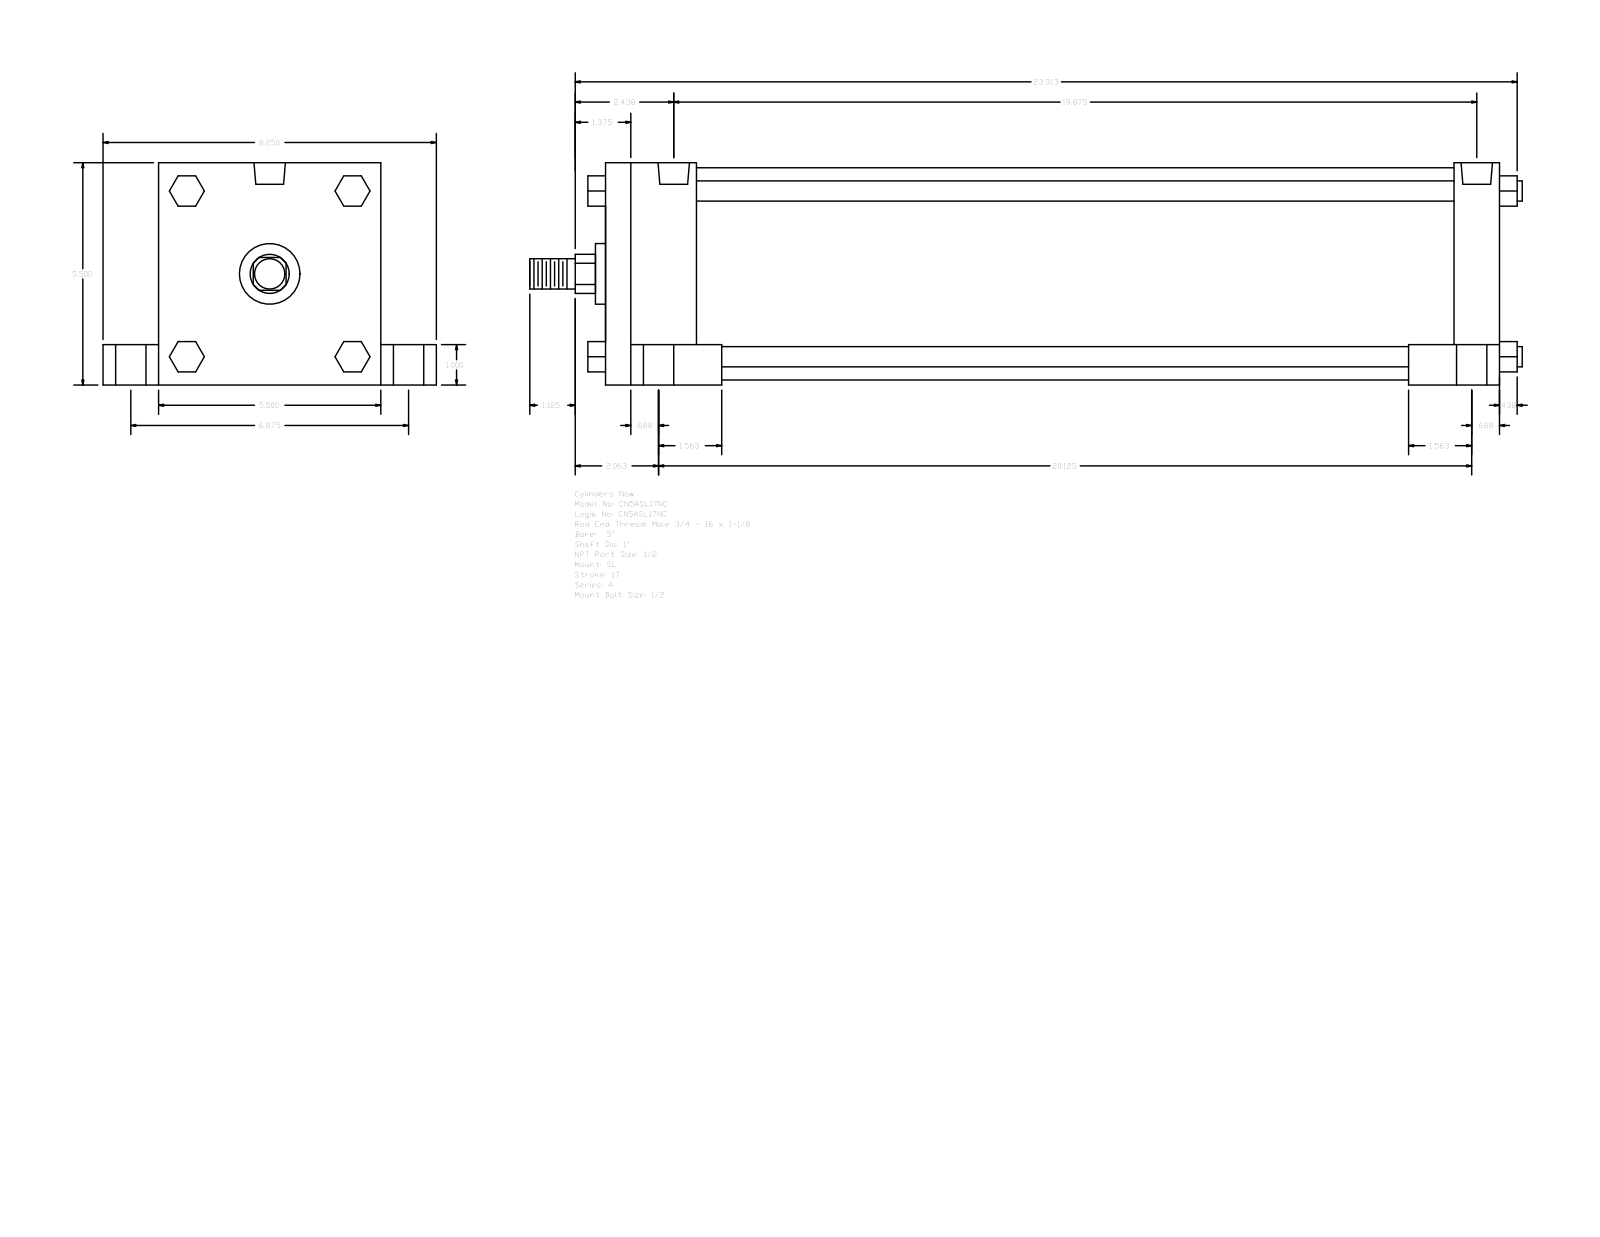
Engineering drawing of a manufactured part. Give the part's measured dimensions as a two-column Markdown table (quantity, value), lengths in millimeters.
| quantity | value |
| --- | --- |
| part name | A_SL__0500_1 |
| STEP written by | GSSL Pune (CONFIG_CONTROL_DESIGN) |
| units | millimeters |
| bodies | 0 solids, 150 faces (114 planar, 36 cylindrical, 0 other) |
| overall size | 623.89 × 209.55 × 139.7 |
| round holes (diameter × count) | 8.73 × 4, 19.05 × 4, 25.4 × 4, 19.77 × 2 |
| round bosses / shafts (diameter × count) | 12.7 × 4, 133.35 × 1, 38.1 × 1, 25.4 × 1, 19.05 × 1 |
| partial cylindrical surfaces (radius × count) | 12.29 × 1 |
| main face-to-face distances | 139.7, 561.97, 28.57, 25.4, 114.3, 34.93, 174.63, 57.15, 533.4, 476.25 |
| hole center spacings | 2.39, 87.31, 87.37, 87.83, 88.12, 174.62, 500.05, 502.44 |
